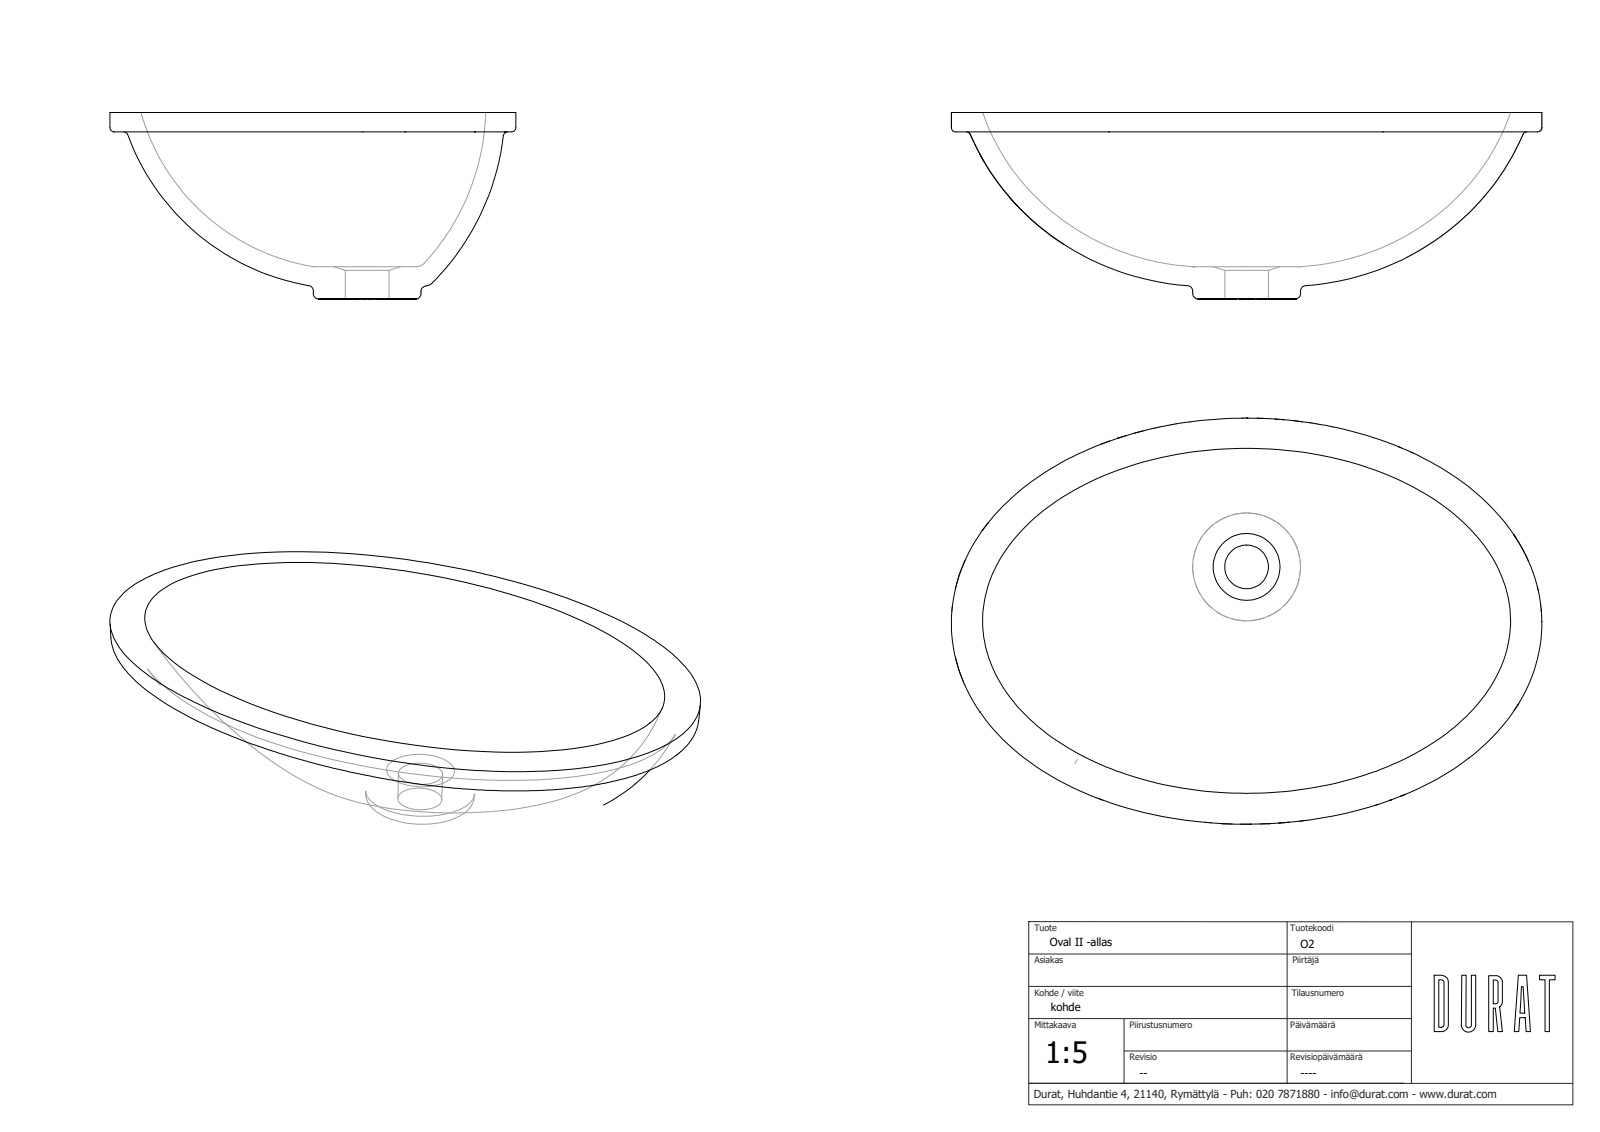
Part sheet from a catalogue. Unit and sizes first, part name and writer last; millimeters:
Units: millimetres
Overall size (bounding box): 548.08 × 376.71 × 173
Main face-to-face distances: 18, 155, 173, 30, 125, 143
Volume: 4 381 000 mm³ · Surface area: 507 041 mm²
Bodies: 1 solid, 27 faces (4 planar, 0 cylindrical, 23 other)
STEP written by: ST-DEVELOPER v15 (AUTOMOTIVE_DESIGN)
